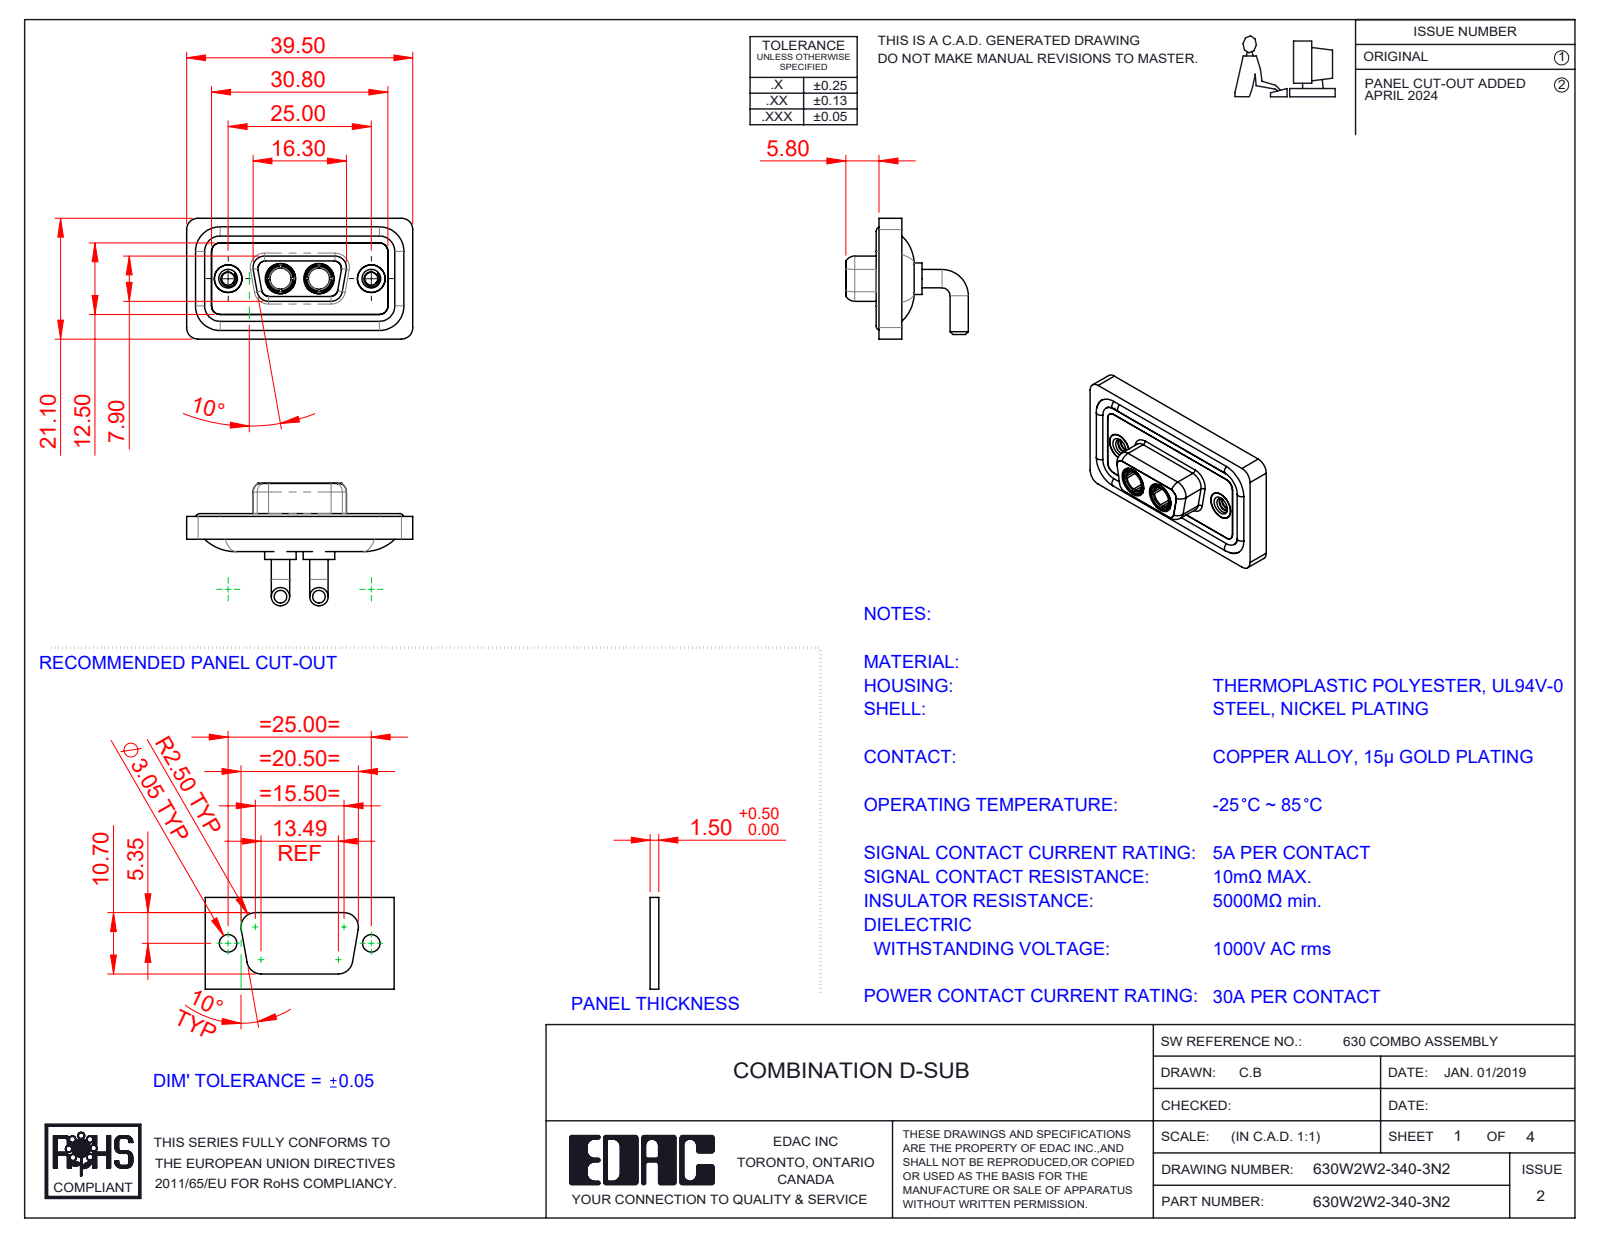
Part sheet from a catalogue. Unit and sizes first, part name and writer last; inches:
Units: inches
Overall size (bounding box): 1.555 × 0.843 × 0.831
Round holes (diameter × count): ⌀0.191 ×4, ⌀0.089 ×2, ⌀0.146 ×2, ⌀0.157 ×2, ⌀0.159 ×2, ⌀0.197 ×2, ⌀0.209 ×2
Round bosses / shafts (diameter × count): ⌀0.126 ×4, ⌀0.063 ×4, ⌀0.217 ×2, ⌀0.205 ×2, ⌀0.195 ×2, ⌀0.195 ×2, ⌀0.189 ×2, ⌀0.187 ×2
Partial cylindrical surfaces — rounded edges, fillets, slot ends (radius × count): R0.059 ×18, R0.079 ×18, R0.053 ×8, R0.063 ×8, R0.01 ×4, R0.02 ×4, R0.024 ×4, R0.026 ×4
Main face-to-face distances: 0.016, 0.071, 0.043, 0.114, 0.098, 0.063, 0.122, 0.059, 0.083, 0.02
Hole centre spacings: 0.36, 0.624, 0.265, 0.984
Volume: 0.297 in³ · Surface area: 12.12 in²
Bodies: 11 solids, 542 faces (163 planar, 238 cylindrical, 141 other)
Part name (STEP PRODUCT): 630Combo Shell Front_09 Contacts; 630Combo Threaded Rivet_2; 630Combo Shell Rear_09 Contacts; Power Socket_30A RA (+3 more)
STEP written by: SolidWorks 2023 (CONFIG_CONTROL_DESIGN)
